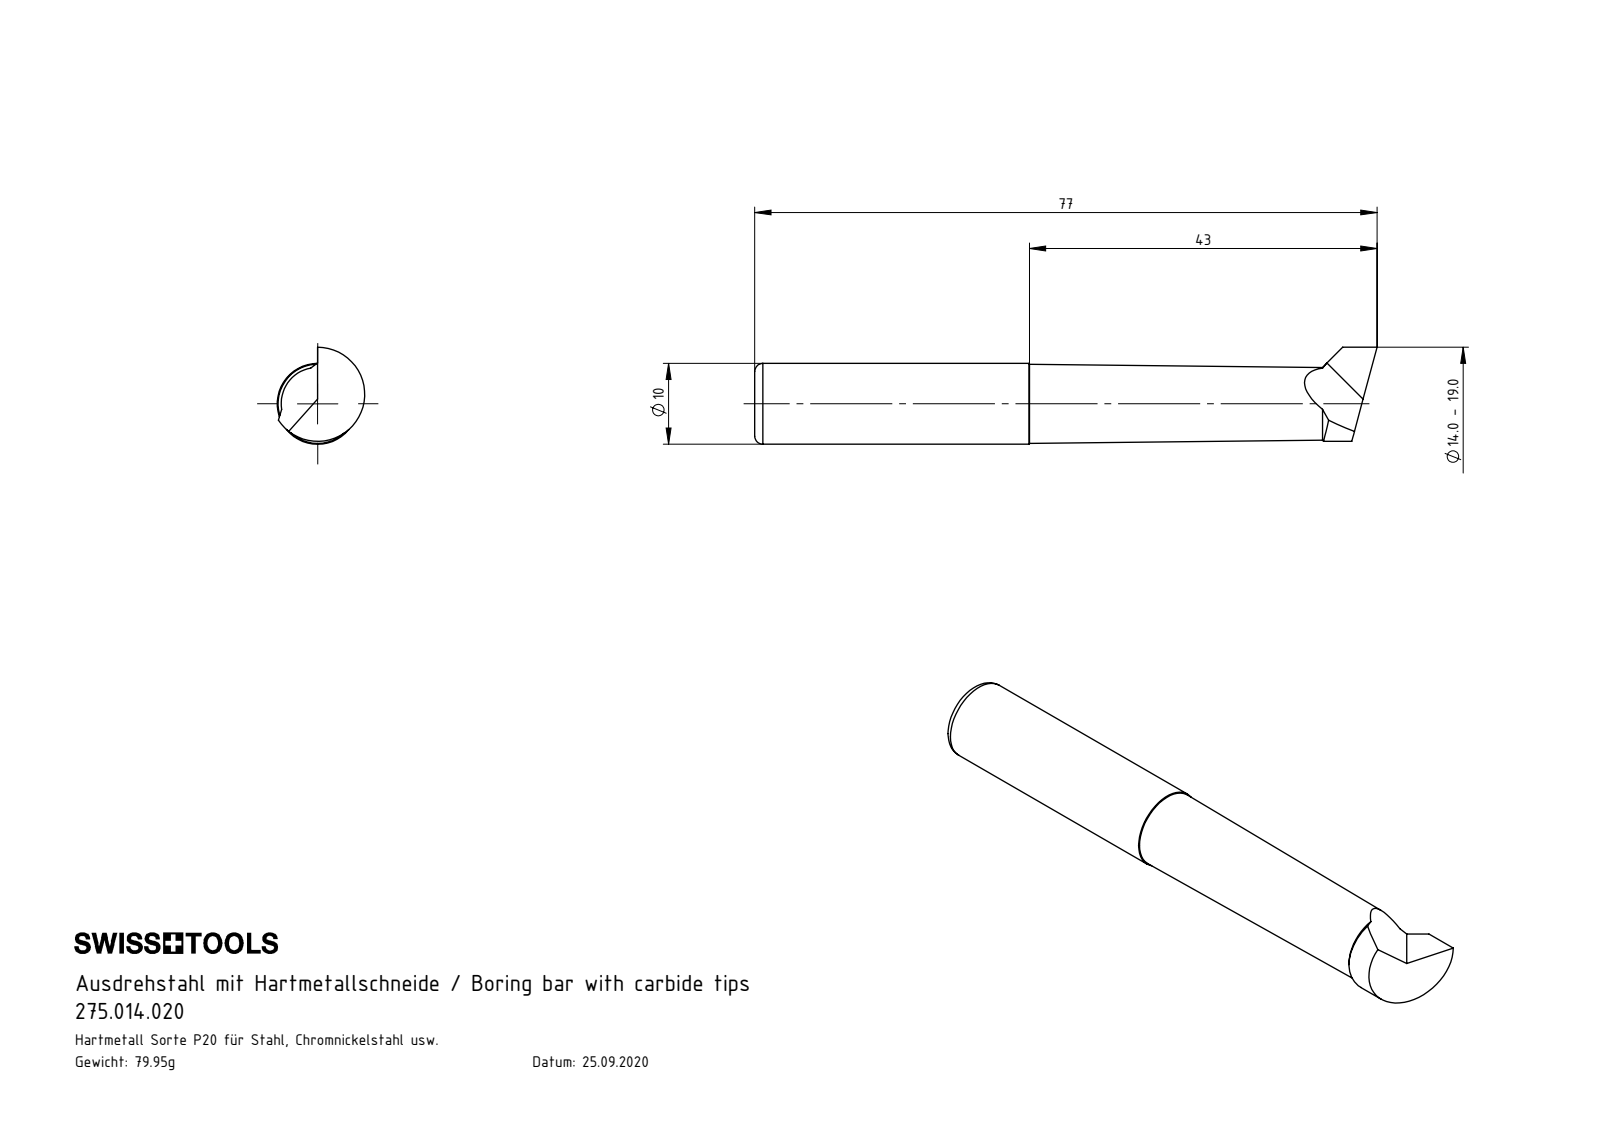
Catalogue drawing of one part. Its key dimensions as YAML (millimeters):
part_name: "275.014.020"
step_written_by: "SolidWorks 2022 (CONFIG_CONTROL_DESIGN)"
units: millimeters
bodies: {solids: 1, faces: 16, planar: 4, cylindrical: 3, other: 9}
overall_size: [77, 12, 10.82]
volume: 5514
surface_area: 2452
round_bosses_or_shafts:
  - {diameter: 10, count: 1}
partial_cylinders:
  - {radius: 5.82, count: 1}
